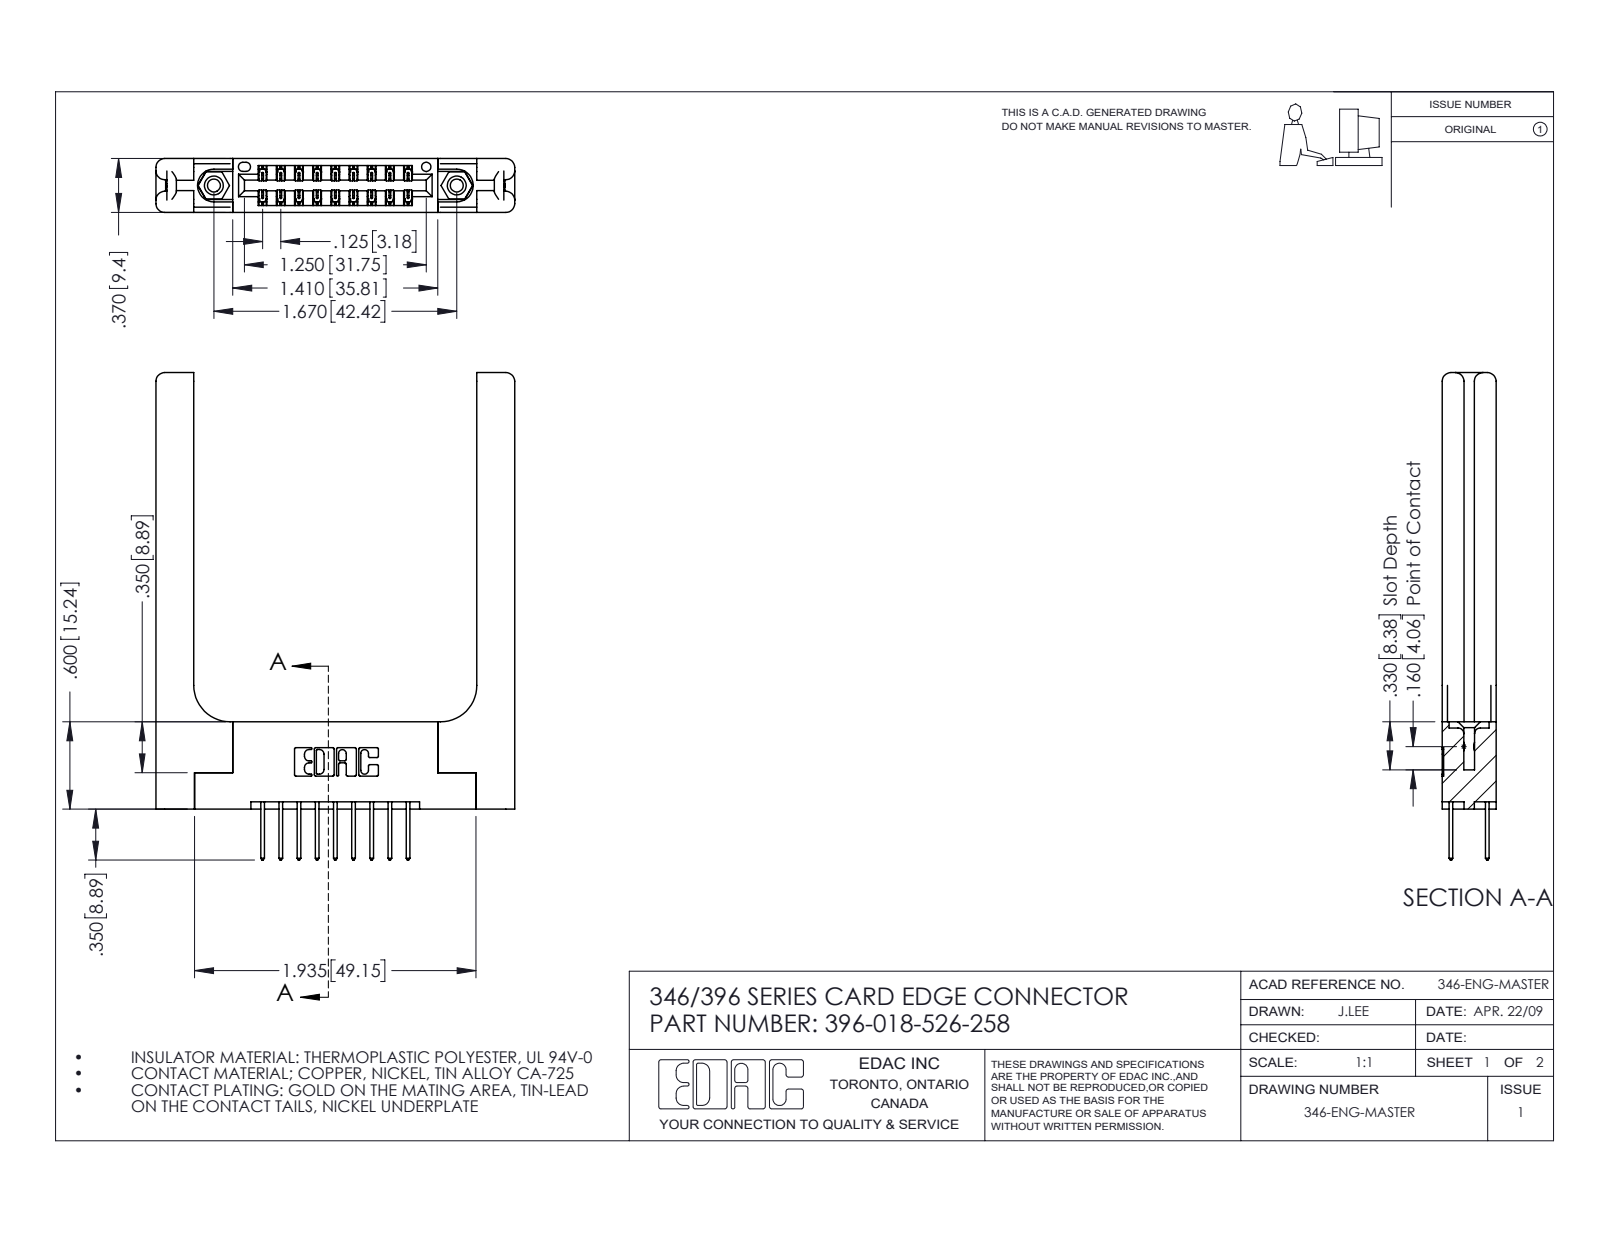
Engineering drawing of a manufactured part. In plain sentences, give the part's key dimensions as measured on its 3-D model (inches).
The part is named "345-250-001_345-250-001-102; 346-220-058_345-220-058; 345-292-001_345-293-126; 396-018-526-258 (+1 more)". Its 3-D file was written by "SolidWorks 2016 (CONFIG_CONTROL_DESIGN)". It is 23 solids with 1314 faces: 854 planar, 400 cylindrical and 60 other. Overall it measures 3.35 by 2.466 by 0.37 inches. Its volume is 0.816 cubic inches and its surface area 19.64 square inches. Round holes: 2 of diameter 0.089, 2 of diameter 0.125, 2 of diameter 0.156, 1 of diameter 0.064. Round bosses or shafts: 2 of diameter 0.155. Partial cylindrical surfaces (rounded edges, fillets, slot ends): 27 of radius 0.006, 22 of radius 0.01, 18 of radius 0.01, 16 of radius 0.06, 6 of radius 0.007, 6 of radius 0.031, 3 of radius 0.026, 2 of radius 0.014. The main face-to-face distances are 0.37, 0.15, 0.072, 0.148, 0.22, 0.25, 0.102, 0.048, 0.322, 0.173. The hole center spacings are 0.246, 1.465, 1.67.
